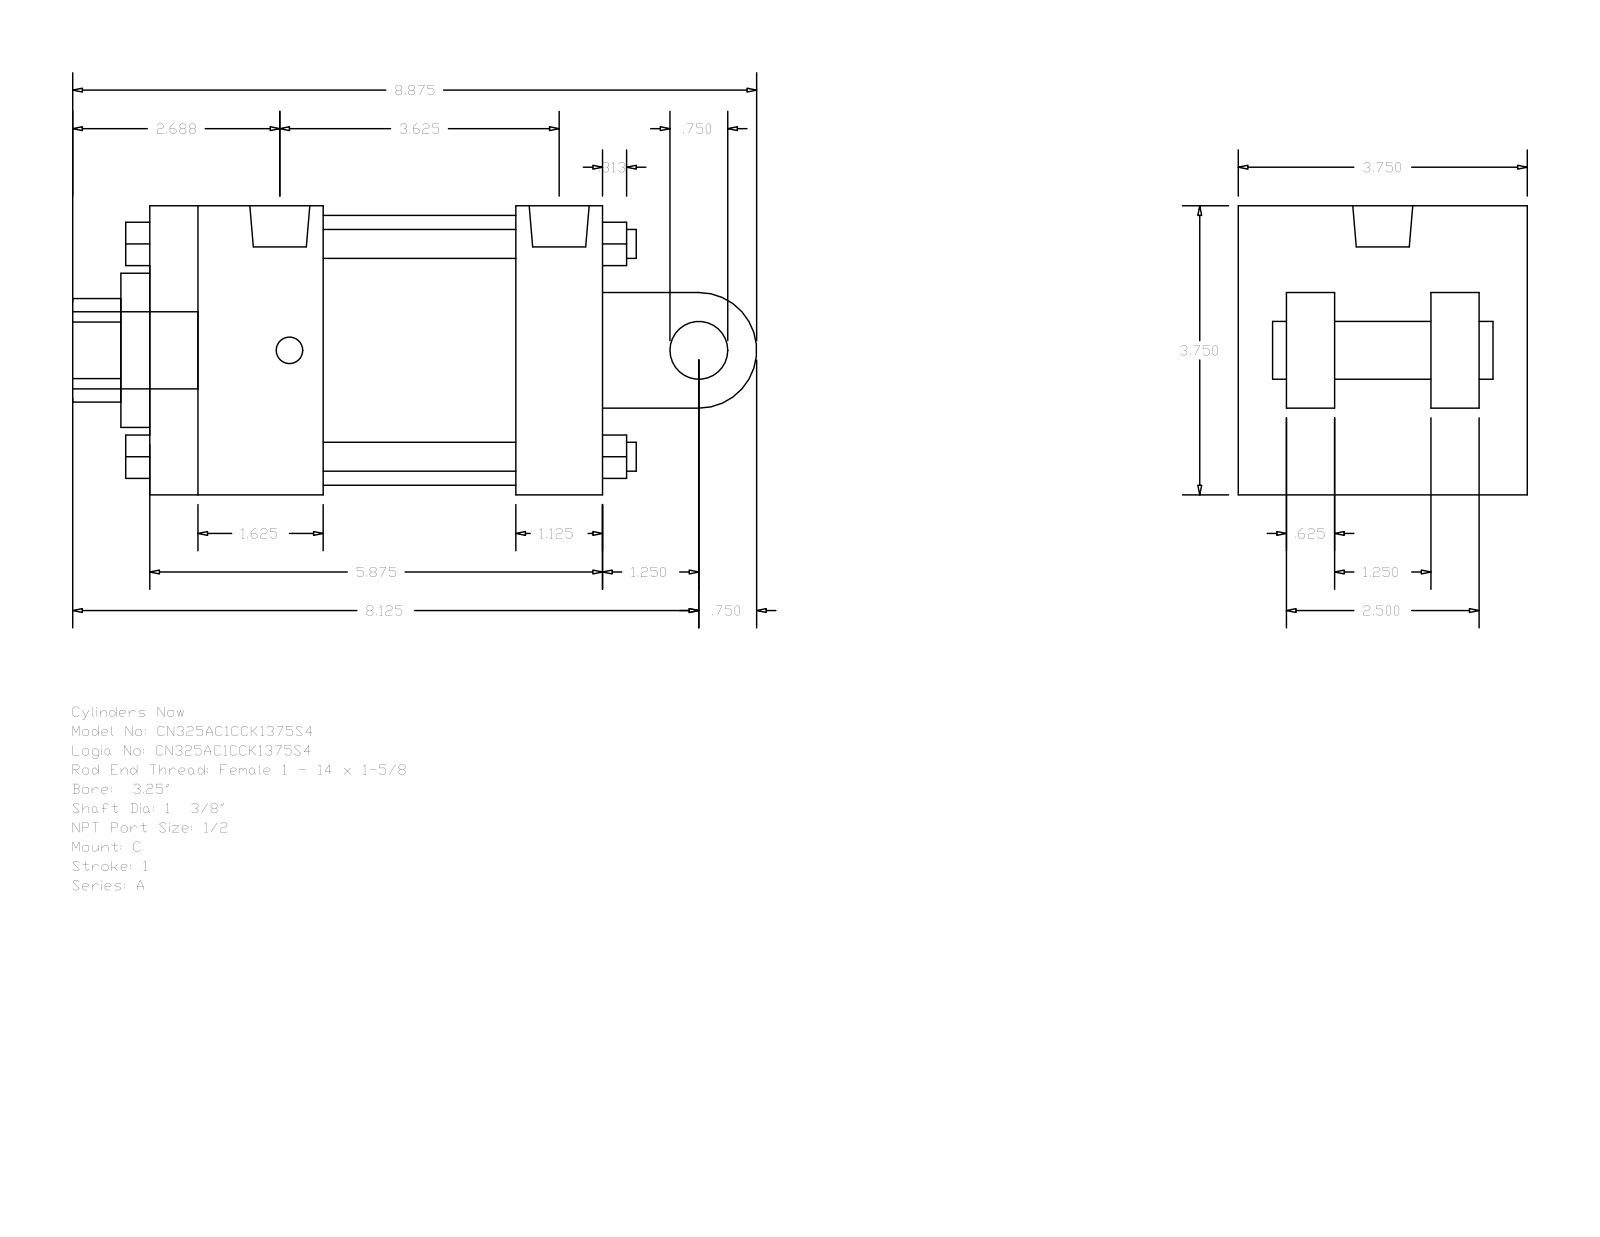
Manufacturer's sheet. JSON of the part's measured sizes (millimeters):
{"part_name": "A_C__0325_1.375", "step_written_by": "GSSL Pune (CONFIG_CONTROL_DESIGN)", "units": "millimeters", "bodies": {"solids": 0, "faces": 135, "planar": 102, "cylindrical": 33, "other": 0}, "overall_size": [225.43, 95.25, 95.25], "round_holes": [[8.73, 2], [19.77, 1], [34.92, 1], [50.8, 1], [88.9, 1]], "round_bosses_or_shafts": [[9.53, 4], [8.73, 2], [25.4, 1], [19.77, 1], [19.05, 1]], "partial_cylinders_radius": [[17.06, 1], [19.05, 1]], "face_to_face_distances": [95.24, 63.5, 15.87, 149.22, 28.57, 66.67, 79.37, 31.74, 47.63, 120.65], "hole_center_spacings": [3.18]}
